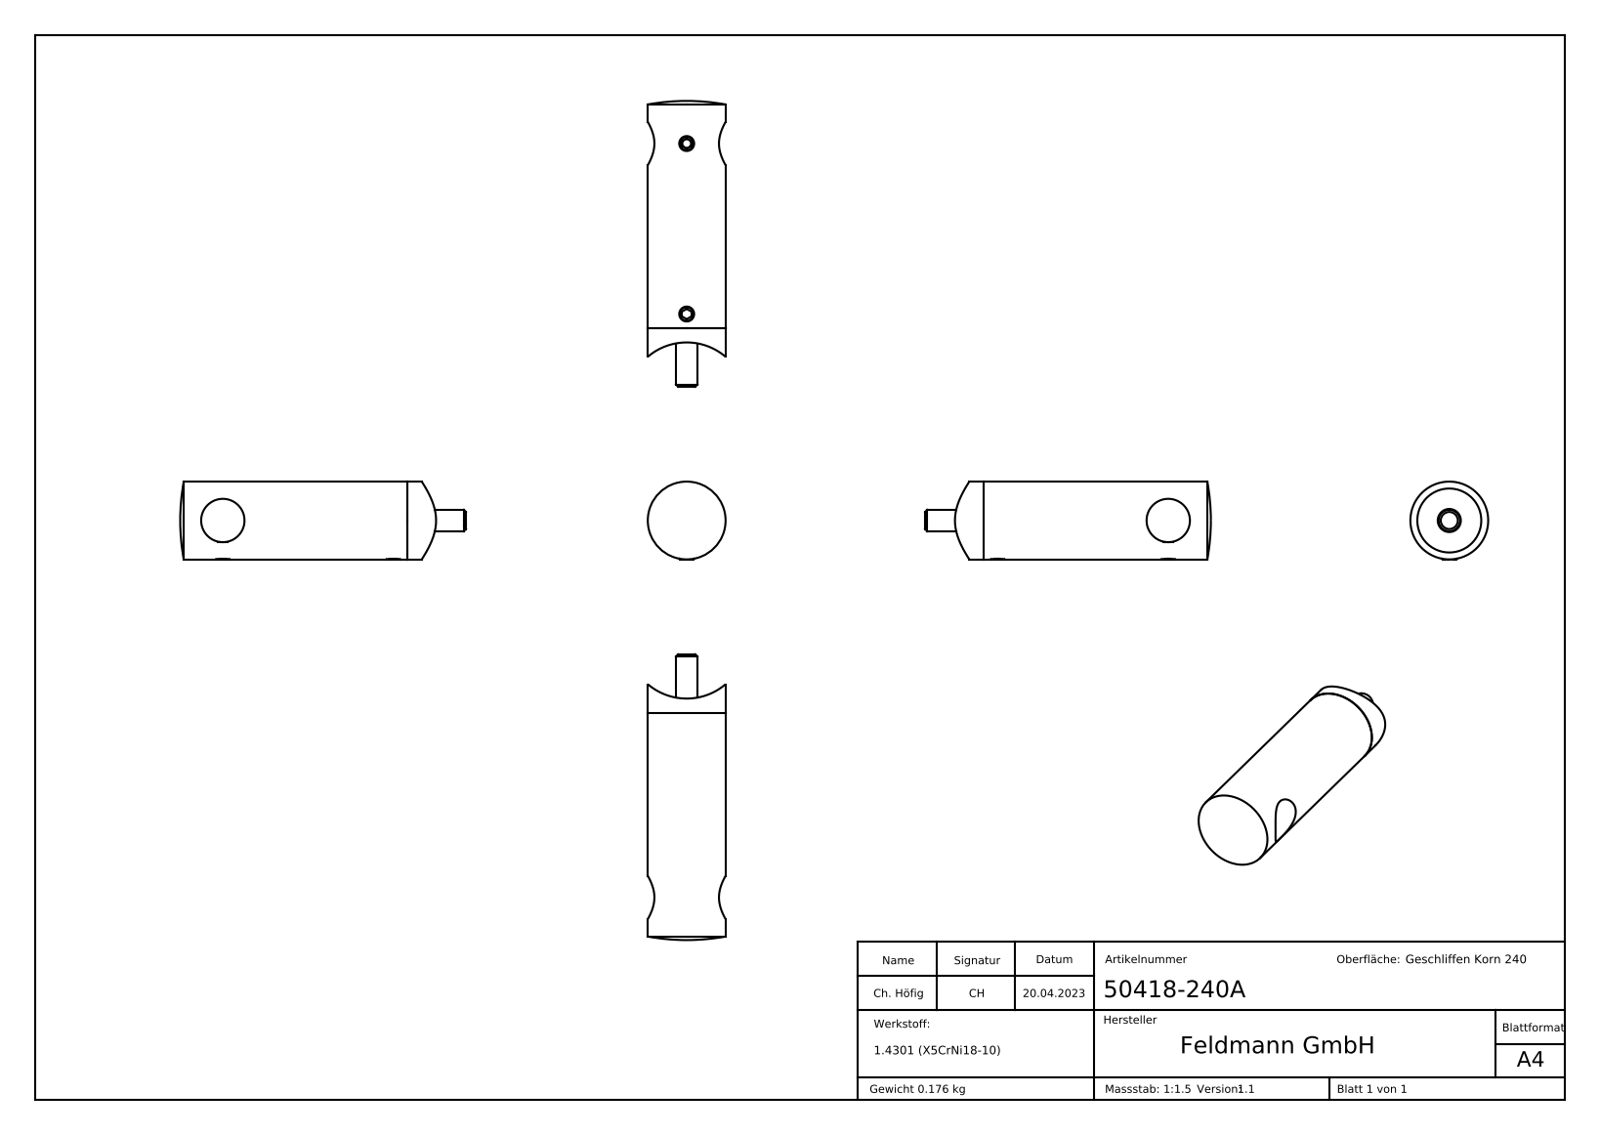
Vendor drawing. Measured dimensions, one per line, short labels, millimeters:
name: 50418-240A; DIN913_DIN 913 M5x5; DIN914_DIN 914 M5x5; DIN7991 M6x25_DIN7991 M6x25 (+2 more)
written by: SolidWorks 2018 (CONFIG_CONTROL_DESIGN)
unit: mm
bodies: 5 solids, 309 faces (183 planar, 15 cylindrical, 111 other)
size: 80.45 × 21.9 × 21.9
volume: 22 287 mm³; area: 8 934 mm²
holes: 2× ⌀4.2, 1× ⌀6.5, 1× ⌀12.2, 1× ⌀18
bosses: 2× ⌀5, 1× ⌀21.9, 1× ⌀12, 1× ⌀6
rounds: 1× R16.85
face distances: 2, 16, 14, 8.55, 10.55, 5.45, 2.5, 4, 14.45, 16.45
hole spacings: 48
